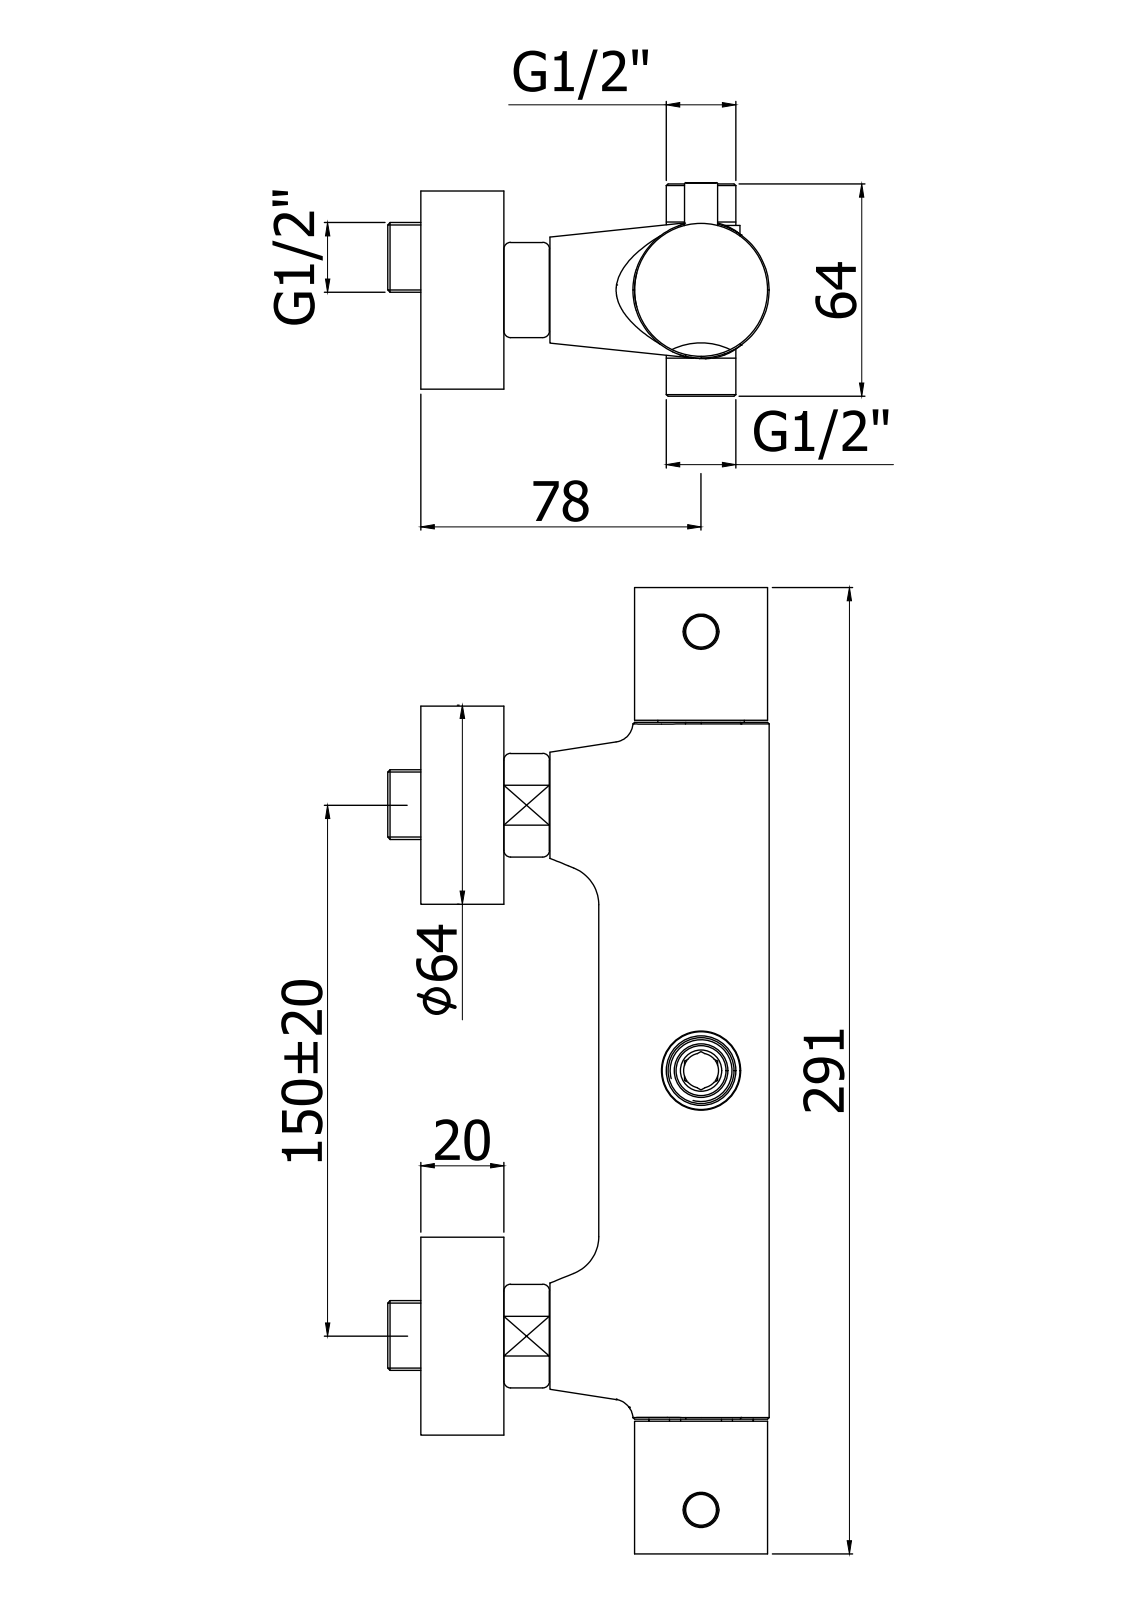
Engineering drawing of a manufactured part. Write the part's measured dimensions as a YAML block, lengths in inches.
part_name: "LIQ169CR"
step_written_by: "CREO PARAMETRIC BY PTC INC, 2020044 (CONFIG_CONTROL_DESIGN)"
units: inches
bodies: {solids: 2, faces: 975, planar: 311, cylindrical: 320, other: 344}
overall_size: [11.328, 4.067, 2.5]
volume: 20.42
surface_area: 216.3
round_holes:
  - {diameter: 0.157, count: 4}
  - {diameter: 0.276, count: 3}
  - {diameter: 0.594, count: 3}
  - {diameter: 0.098, count: 2}
  - {diameter: 0.118, count: 2}
  - {diameter: 0.128, count: 2}
  - {diameter: 0.197, count: 2}
  - {diameter: 0.236, count: 2}
  - {diameter: 0.413, count: 2}
  - {diameter: 0.63, count: 2}
  - {diameter: 1.417, count: 2}
  - {diameter: 0.244, count: 1}
round_bosses_or_shafts:
  - {diameter: 2.5, count: 2}
  - {diameter: 1.575, count: 2}
  - {diameter: 0.835, count: 2}
  - {diameter: 0.748, count: 2}
  - {diameter: 0.315, count: 2}
  - {diameter: 0.299, count: 2}
  - {diameter: 1.638, count: 1}
  - {diameter: 0.906, count: 1}
partial_cylinders:
  - {radius: 0.059, count: 64}
  - {radius: 0.039, count: 6}
  - {radius: 0.069, count: 4}
  - {radius: 0.108, count: 2}
  - {radius: 0.157, count: 2}
  - {radius: 0.256, count: 2}
  - {radius: 0.335, count: 2}
  - {radius: 0.614, count: 2}
face_to_face_distances: [0.787, 0.118, 2.429, 1.642, 2.547, 1.76, 0.128, 0.119, 0.433, 1.398]
hole_center_spacings: [0.197, 0.339, 0.388, 0.513, 0.53, 0.596, 0.863, 0.236]
